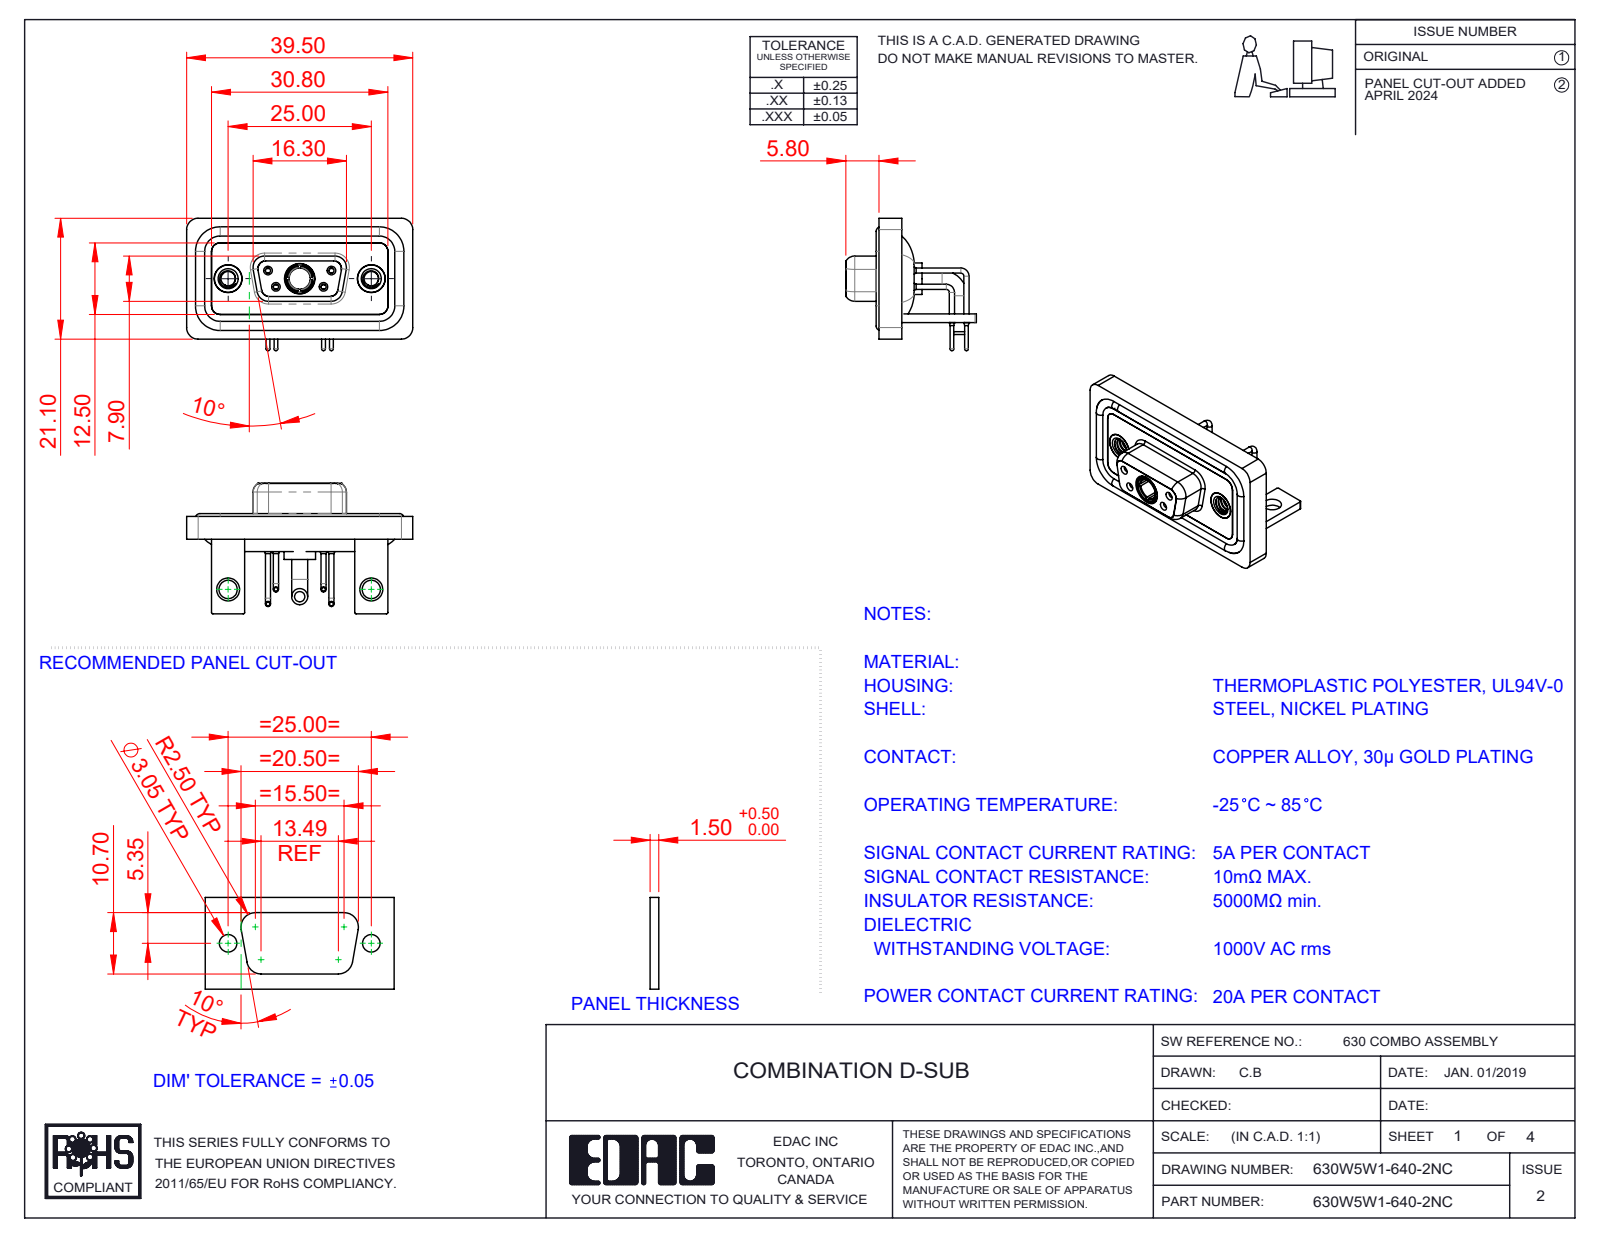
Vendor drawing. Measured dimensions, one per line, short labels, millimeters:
name: 630Combo Shell Front_09 Contacts; 630Combo Stabilizer Bracket_50 Contacts; 630Combo Contact Row 1_50 Contacts; 630Combo Shell Rear_09 Contacts (+6 more)
written by: SolidWorks 2023 (CONFIG_CONTROL_DESIGN)
unit: mm
bodies: 15 solids, 718 faces (214 planar, 327 cylindrical, 177 other)
size: 39.5 × 23.12 × 22.8
volume: 5 188 mm³; area: 8 582 mm²
holes: 4× ⌀0.9, 4× ⌀1.1, 4× ⌀1.5, 4× ⌀2, 3× ⌀4.85, 2× ⌀1.6, 2× ⌀1.7, 2× ⌀2.5, 2× ⌀3.2, 2× ⌀4, 2× ⌀4.05, 2× ⌀5
bosses: 6× ⌀1.6, 4× ⌀0.9, 4× ⌀0.65, 2× ⌀4.95, 2× ⌀4.8, 2× ⌀2.8, 1× ⌀5.5, 1× ⌀5.2
rounds: 19× R2, 18× R1.5, 16× R0.25, 8× R1.35, 8× R1.6, 5× R0.5, 4× R0.6, 4× R0.65
face distances: 0.4, 2.9, 1.5, 1.8, 1.1, 3.7, 1.6, 0.8, 2.5, 3.1
hole spacings: 3.16, 5.72, 7.1, 12.5, 18.1, 25, 4.39, 4.4
